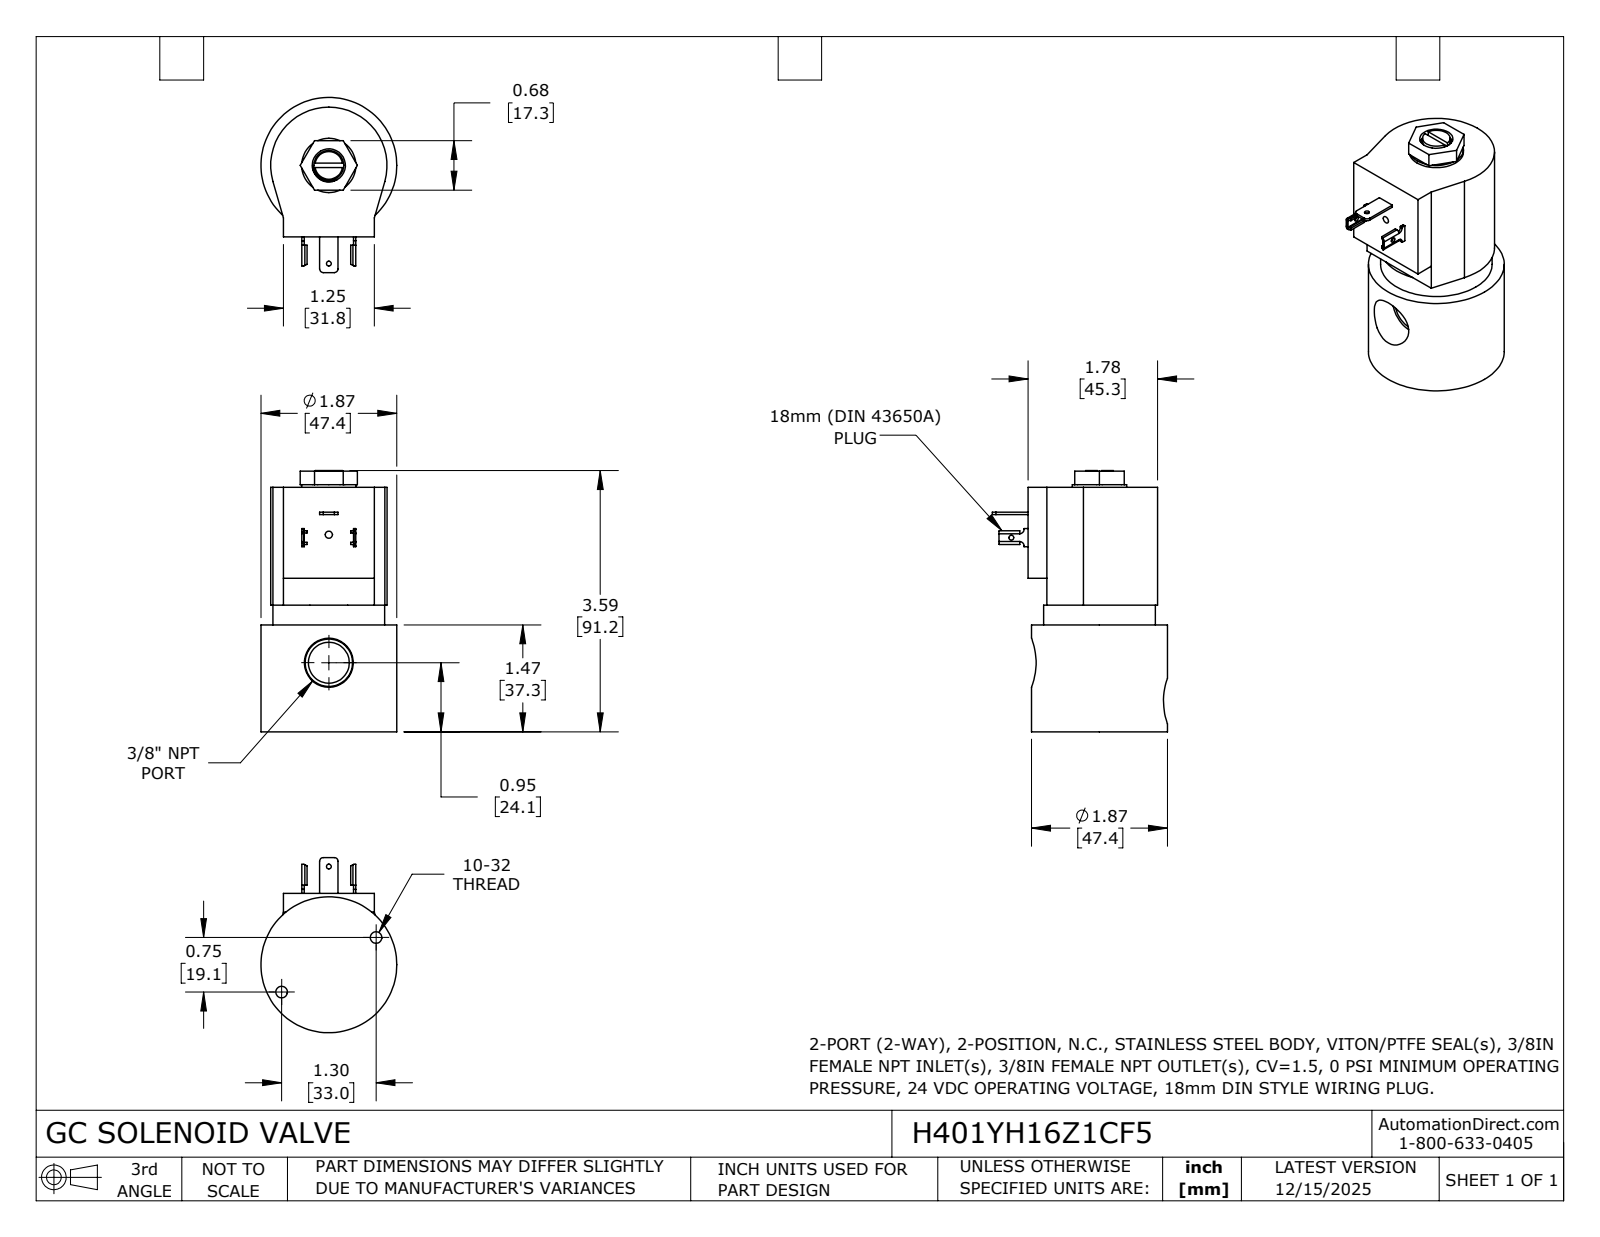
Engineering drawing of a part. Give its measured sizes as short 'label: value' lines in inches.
name: H401YH16Z1CF5
written by: SolidWorks 2024 (CONFIG_CONTROL_DESIGN)
unit: in
bodies: 1 solid, 203 faces (80 planar, 98 cylindrical, 25 other)
size: 3.591 × 2.407 × 1.868
volume: 7.989 in³; area: 30.19 in²
holes: 2× ⌀0.159, 2× ⌀0.562, 1× ⌀0.066, 1× ⌀0.067, 1× ⌀0.1, 1× ⌀0.456
bosses: 1× ⌀1.868, 1× ⌀1.535, 1× ⌀0.746, 1× ⌀0.38
rounds: 4× R0.006, 4× R0.041, 2× R0.05, 2× R0.06, 1× R0.8
face distances: 3.36, 1.47, 1.89, 0.26, 2.11, 0.64, 1.25, 1.25, 1.62, 3.583
hole spacings: 0.75, 0.527, 1.171, 1.35, 1.5, 1.759, 1.843, 2.286
